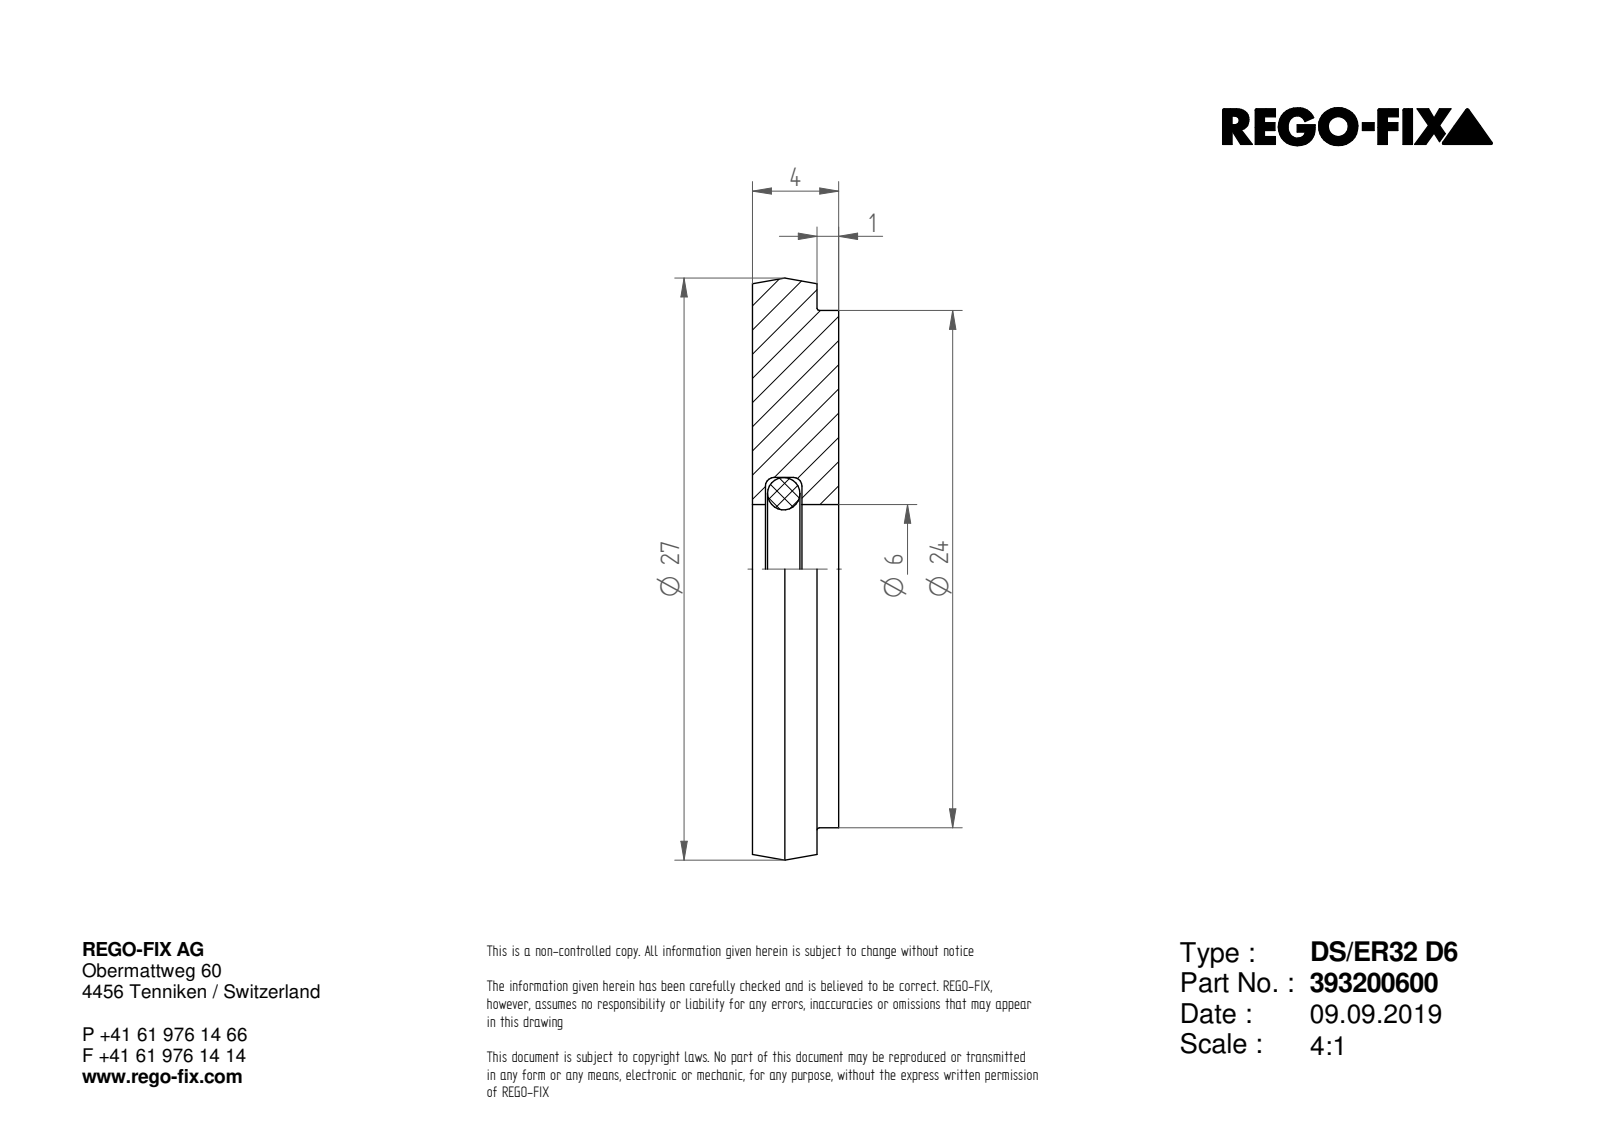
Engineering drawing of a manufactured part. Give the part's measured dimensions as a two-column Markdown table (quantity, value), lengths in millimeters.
| quantity | value |
| --- | --- |
| part name | NOCUT |
| STEP written by | SIEMENS PLM Software Solid Edge ST10 (AUTOMOTIVE_DESIGN) |
| units | millimeters |
| bodies | 1 solid, 7 faces (3 planar, 3 cylindrical, 1 other) |
| overall size | 27 × 27 × 4 |
| volume | 2 057 mm³ |
| surface area | 1 491 mm² |
| round holes (diameter × count) | 6 × 1 |
| round bosses / shafts (diameter × count) | 27 × 1, 24 × 1 |
| main face-to-face distances | 4, 1, 3 |
